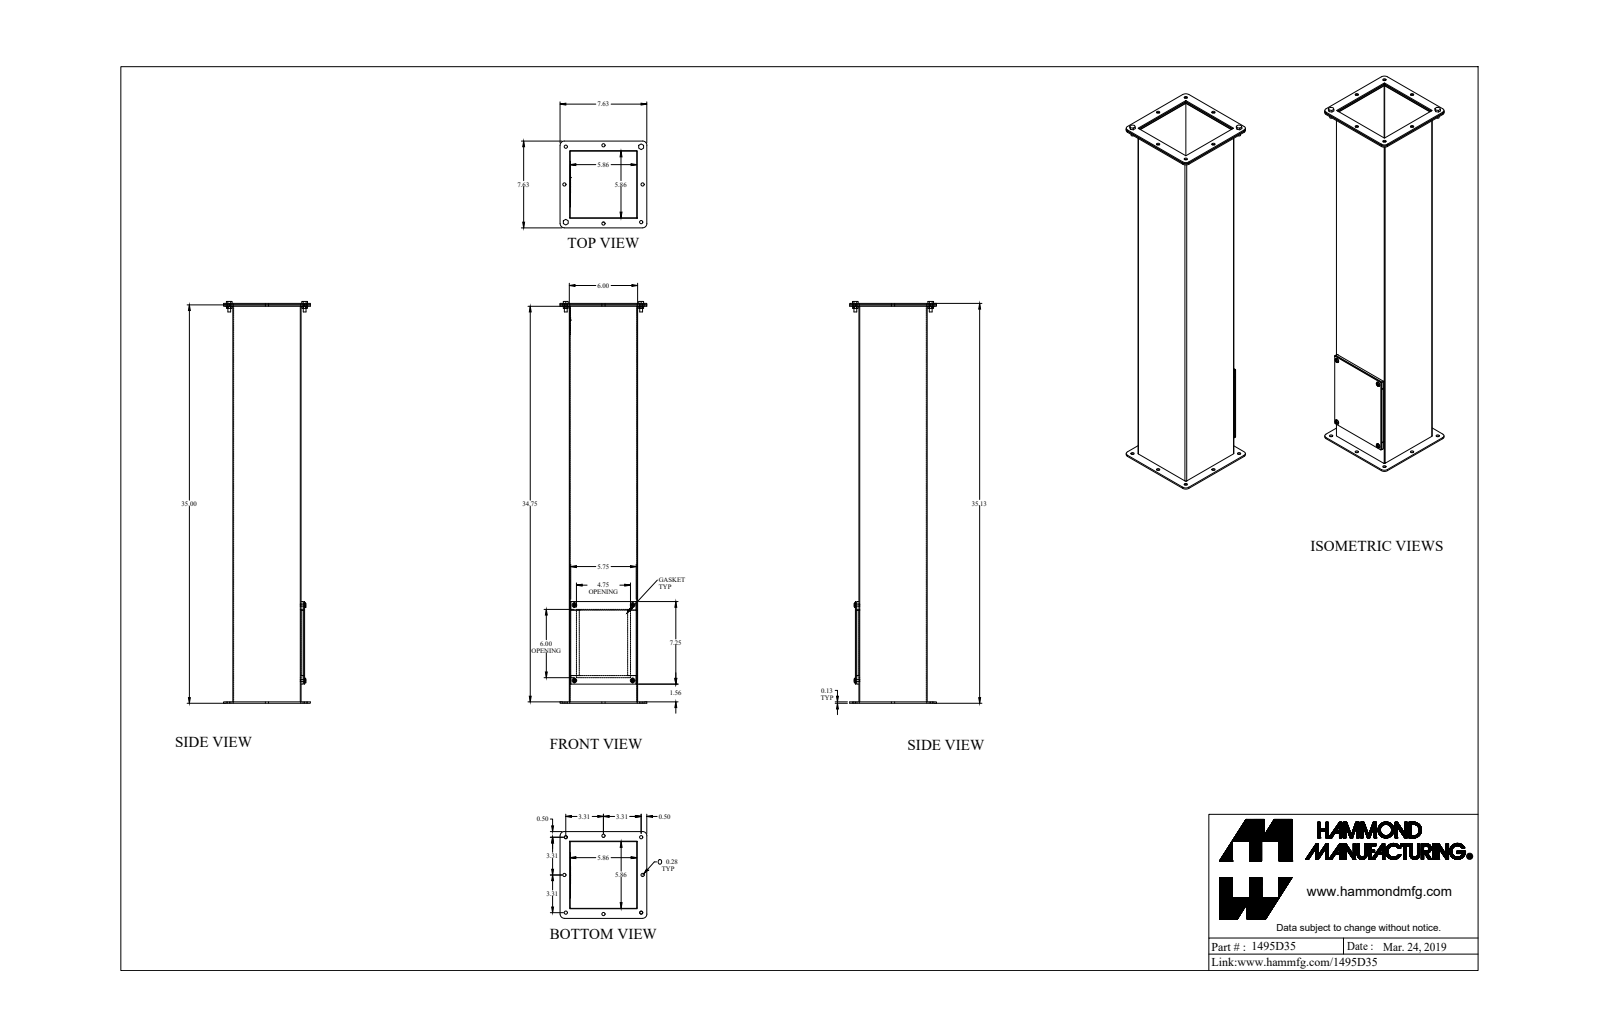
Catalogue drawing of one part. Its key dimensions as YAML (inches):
part_name: "1495D35_Default"
step_written_by: "SolidWorks 2019 (CONFIG_CONTROL_DESIGN)"
units: inches
bodies: {solids: 21, faces: 369, planar: 227, cylindrical: 112, other: 30}
overall_size: [35.299, 7.625, 7.625]
volume: 71.27
surface_area: 1891
round_holes:
  - {diameter: 0.281, count: 8}
  - {diameter: 0.173, count: 4}
  - {diameter: 0.25, count: 4}
  - {diameter: 0.196, count: 3}
round_bosses_or_shafts:
  - {diameter: 0.402, count: 5}
  - {diameter: 0.18, count: 5}
  - {diameter: 0.246, count: 3}
partial_cylinders:
  - {radius: 0.375, count: 4}
  - {radius: 0.036, count: 2}
  - {radius: 0.108, count: 2}
face_to_face_distances: [0.072, 5.928, 6, 5.856, 0.072, 5.856, 5.928, 0.25, 34.875, 0.125]
hole_center_spacings: [7.519, 3.315, 5.125, 5.126, 6.625, 6.625, 3.315, 3.437]
